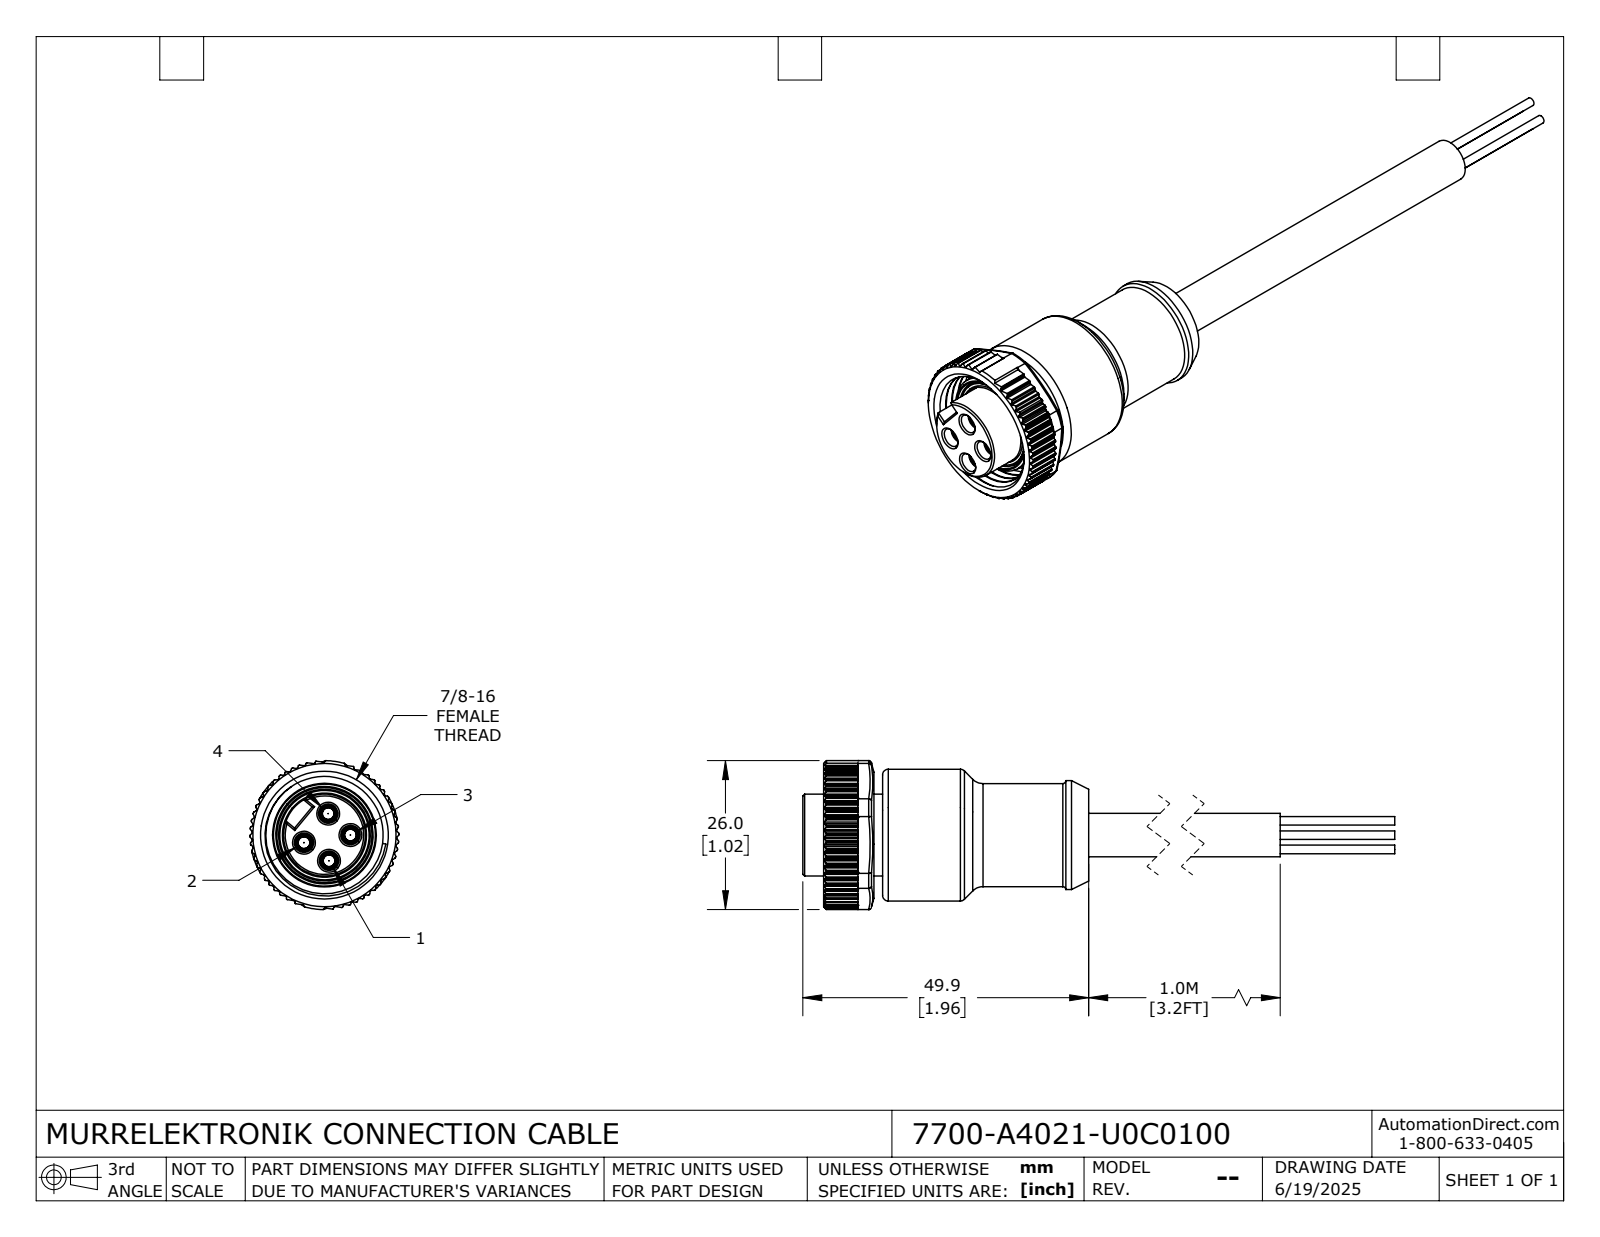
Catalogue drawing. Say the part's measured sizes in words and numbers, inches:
The part is named "7700-A4021-U0C0100". Its 3-D file was written by "SolidWorks 2024 (CONFIG_CONTROL_DESIGN)". It is 1 solid with 674 faces: 296 planar, 293 cylindrical and 85 other. Overall it measures 5.508 by 1.024 by 1.024 inches. Its volume is 1.146 cubic inches and its surface area 12.9 square inches. Round holes: 4 of diameter 0.081, 4 of diameter 0.118, 4 of diameter 0.134, 1 of diameter 0.61, 1 of diameter 0.614, 1 of diameter 0.807, 1 of diameter 0.875. Round bosses or shafts: 4 of diameter 0.059, 1 of diameter 0.906, 1 of diameter 0.748, 1 of diameter 0.713, 1 of diameter 0.709, 1 of diameter 0.701, 1 of diameter 0.563, 1 of diameter 0.299. Partial cylindrical surfaces (rounded edges, fillets, slot ends): 126 of radius 0.008, 16 of radius 0.012, 4 of radius 0.004, 4 of radius 0.029, 1 of radius 0.512. The main face-to-face distances are 0.059, 1.476, 1.417, 0.142, 0.346, 0.406, 1.823, 0.488, 0.547, 1.965. The hole center spacings are 0.15, 0.179, 0.324, 0.212, 0.213, 0.23, 0.26.
